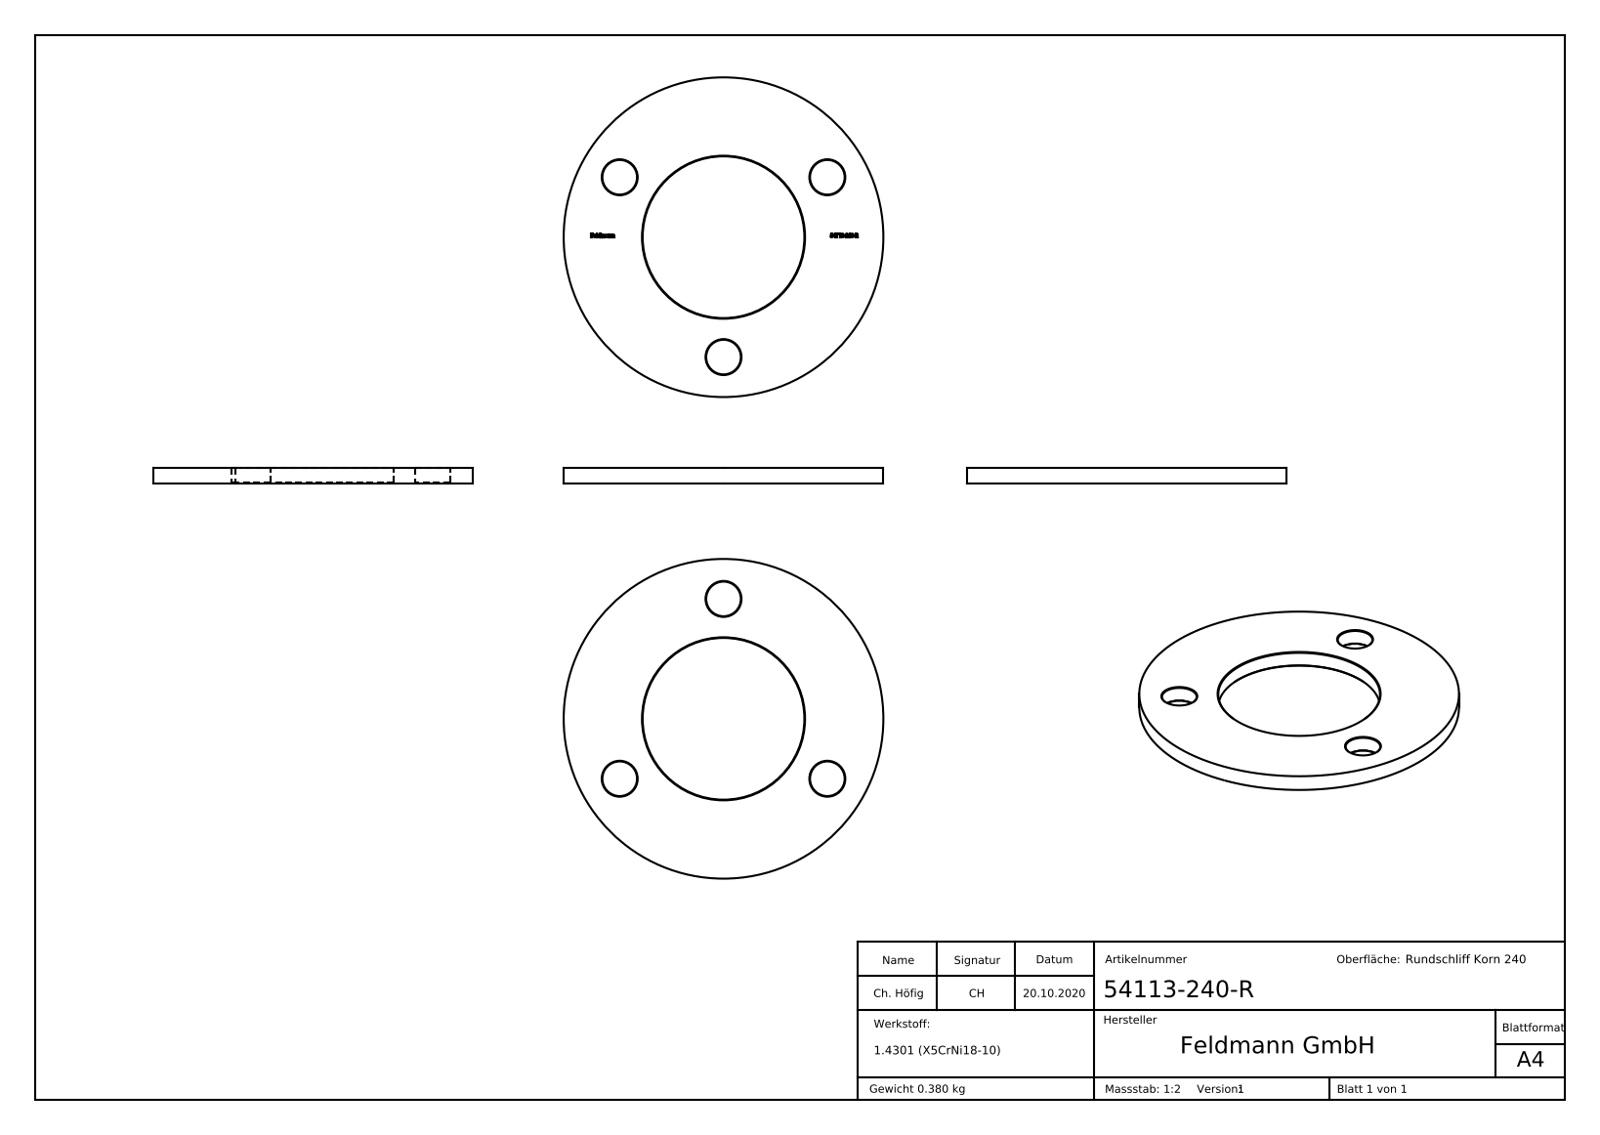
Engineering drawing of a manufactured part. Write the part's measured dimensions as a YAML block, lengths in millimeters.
part_name: "54113-240-R"
step_written_by: "SolidWorks 2018 (CONFIG_CONTROL_DESIGN)"
units: millimeters
bodies: {solids: 1, faces: 270, planar: 154, cylindrical: 10, other: 106}
overall_size: [120, 120, 6]
volume: 48086
surface_area: 20096
round_holes:
  - {diameter: 13, count: 3}
  - {diameter: 60.7, count: 1}
round_bosses_or_shafts:
  - {diameter: 120, count: 1}
face_to_face_distances: [6, 5.9, 0.88, 0.44, 1.02, 2.02, 97.15, 99.17, 0.58, 92.13]
hole_center_spacings: [45, 77.94]
